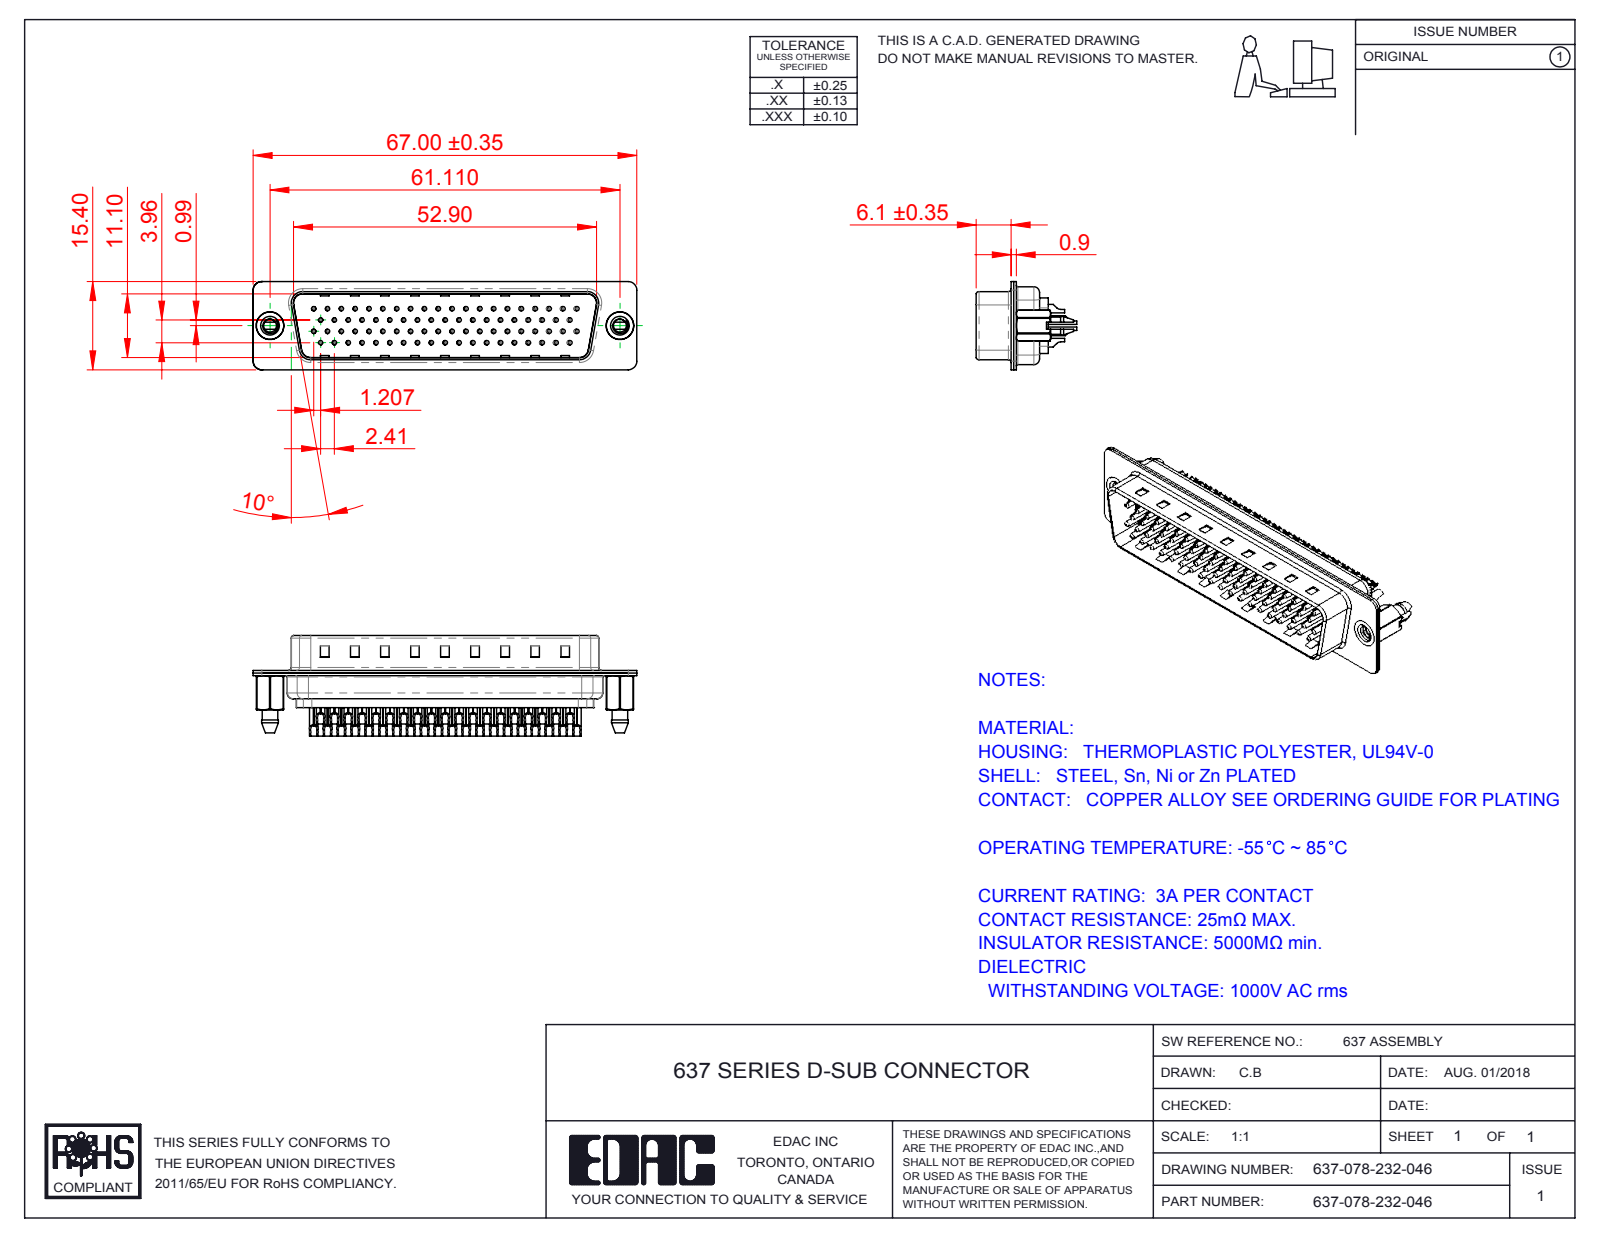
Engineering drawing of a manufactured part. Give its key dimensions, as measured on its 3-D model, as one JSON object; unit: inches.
{"part_name": "637 4-40 Threaded Boardlock_LP; 637 Contact Row 2_32(78); 637 Shell Front_78 Contacts; 637 Housing_78 Contacts (+5 more)", "step_written_by": "SolidWorks 2016 (CONFIG_CONTROL_DESIGN)", "units": "inches", "bodies": {"solids": 83, "faces": 5478, "planar": 1327, "cylindrical": 2435, "other": 1716}, "overall_size": [2.638, 0.691, 0.606], "volume_in3": 0.277, "surface_area_in2": 26.45, "round_holes": [[0.063, 150], [0.014, 78], [0.043, 78], [0.03, 72], [0.079, 72], [0.157, 3], [0.089, 2], [0.189, 2]], "round_bosses_or_shafts": [[0.079, 78], [0.059, 78], [0.03, 78], [0.193, 2], [0.189, 1]], "partial_cylinders_radius": [[0.059, 18], [0.079, 12], [0.02, 8], [0.039, 8], [0.063, 6], [0.01, 4], [0.022, 4], [0.028, 4]], "face_to_face_distances": [0.018, 0.016, 0.059, 0.077, 0.469, 0.453, 0.028, 0.437, 0.035, 0.031], "hole_center_spacings": [0.095, 0.285, 0.239, 0.38, 0.274, 0.333, 0.572, 0.665]}
